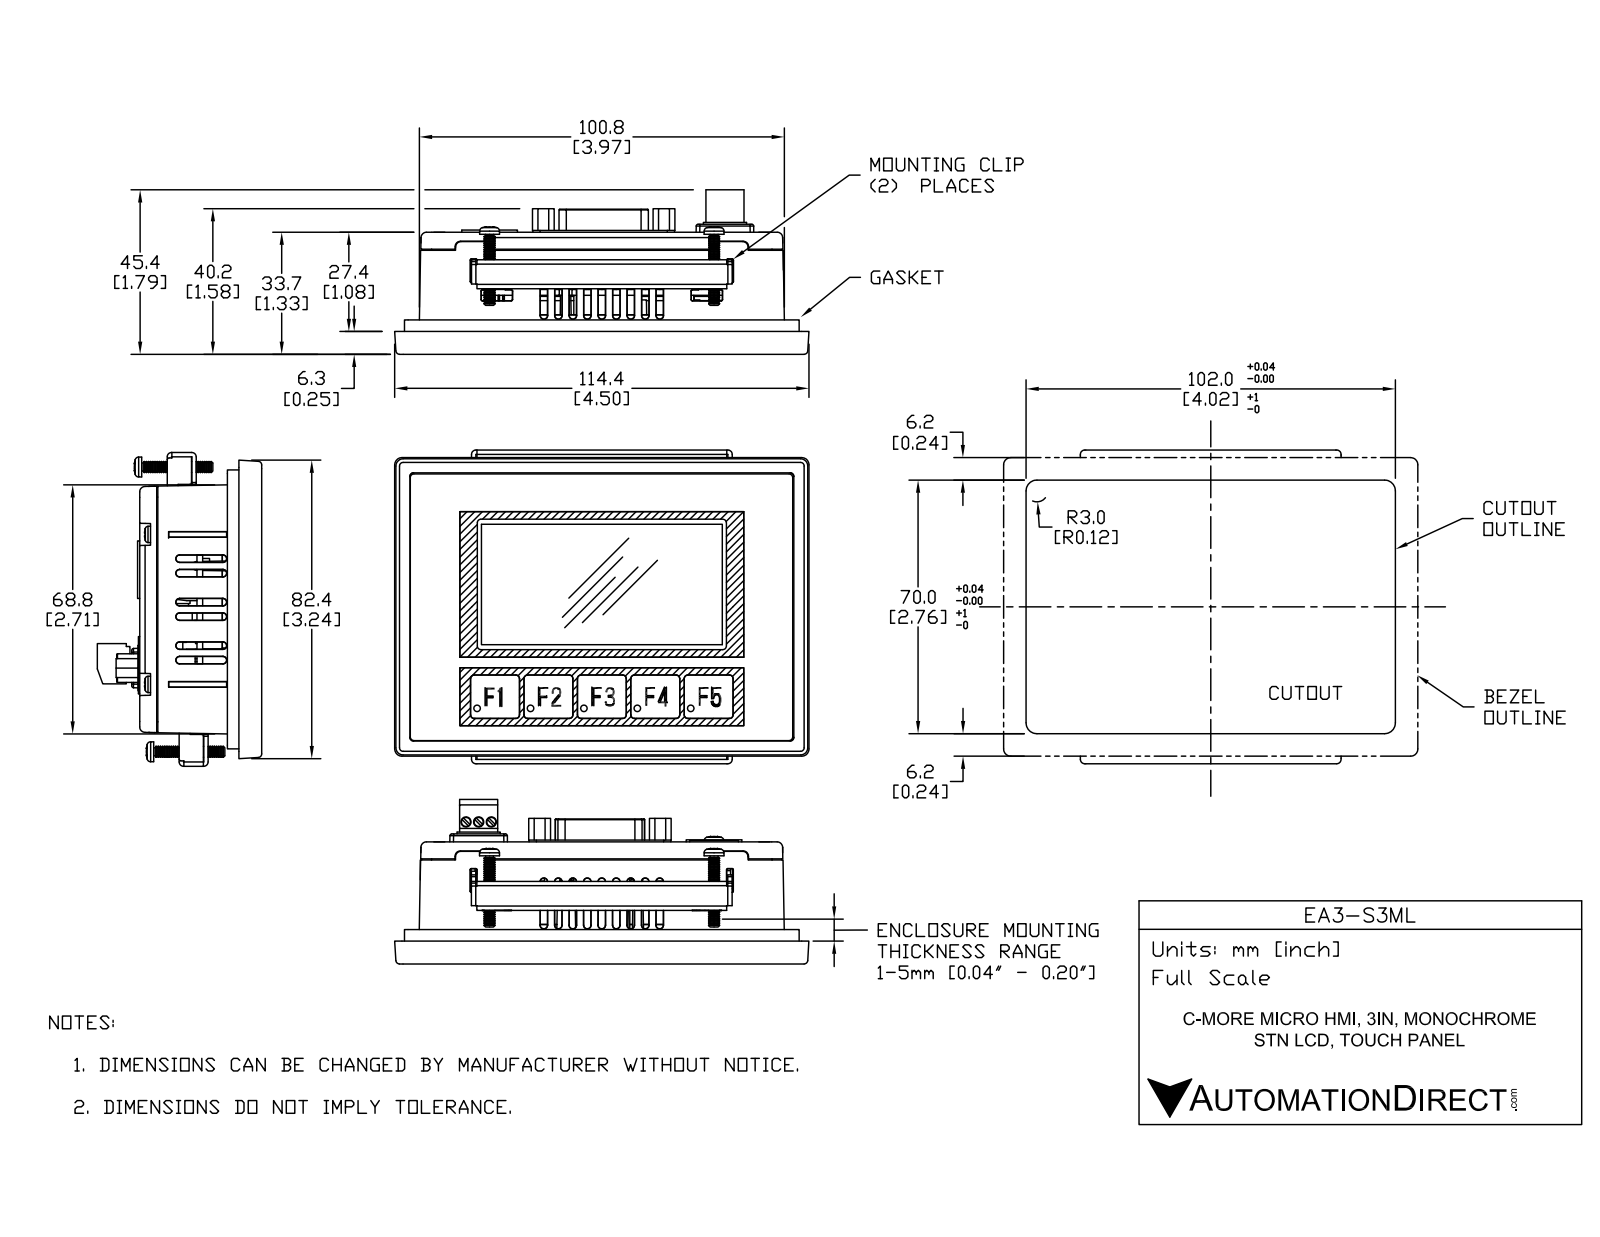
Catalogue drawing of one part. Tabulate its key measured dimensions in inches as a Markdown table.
| quantity | value |
| --- | --- |
| part name | EA3_S3ML |
| STEP written by | SolidWorks 2017 (AUTOMOTIVE_DESIGN) |
| units | inches |
| bodies | 1 solid, 3102 faces (2226 planar, 453 cylindrical, 423 other) |
| overall size | 4.504 × 3.409 × 1.583 |
| volume | 15.28 in³ |
| surface area | 81.73 in² |
| round holes (diameter × count) | 0.039 × 15, 0.071 × 5, 0.122 × 4, 0.097 × 2, 0.102 × 2, 0.12 × 2 |
| round bosses / shafts (diameter × count) | 0.217 × 4, 0.177 × 4, 0.118 × 4, 0.087 × 4, 0.031 × 3, 0.12 × 2 |
| partial cylindrical surfaces (radius × count) | 0.02 × 49, 0.039 × 42, 0.012 × 32, 0.008 × 18, 0.016 × 16, 0.059 × 12, 0.079 × 12, 0.118 × 10 |
| main face-to-face distances | 0.047, 1.318, 1.313, 0.268, 1.306, 0.248, 0.98, 0.36, 0.315, 0.365 |
| hole center spacings | 0.125, 0.109, 0.218, 0.198, 0.198, 0.294, 0.327, 0.398 |
